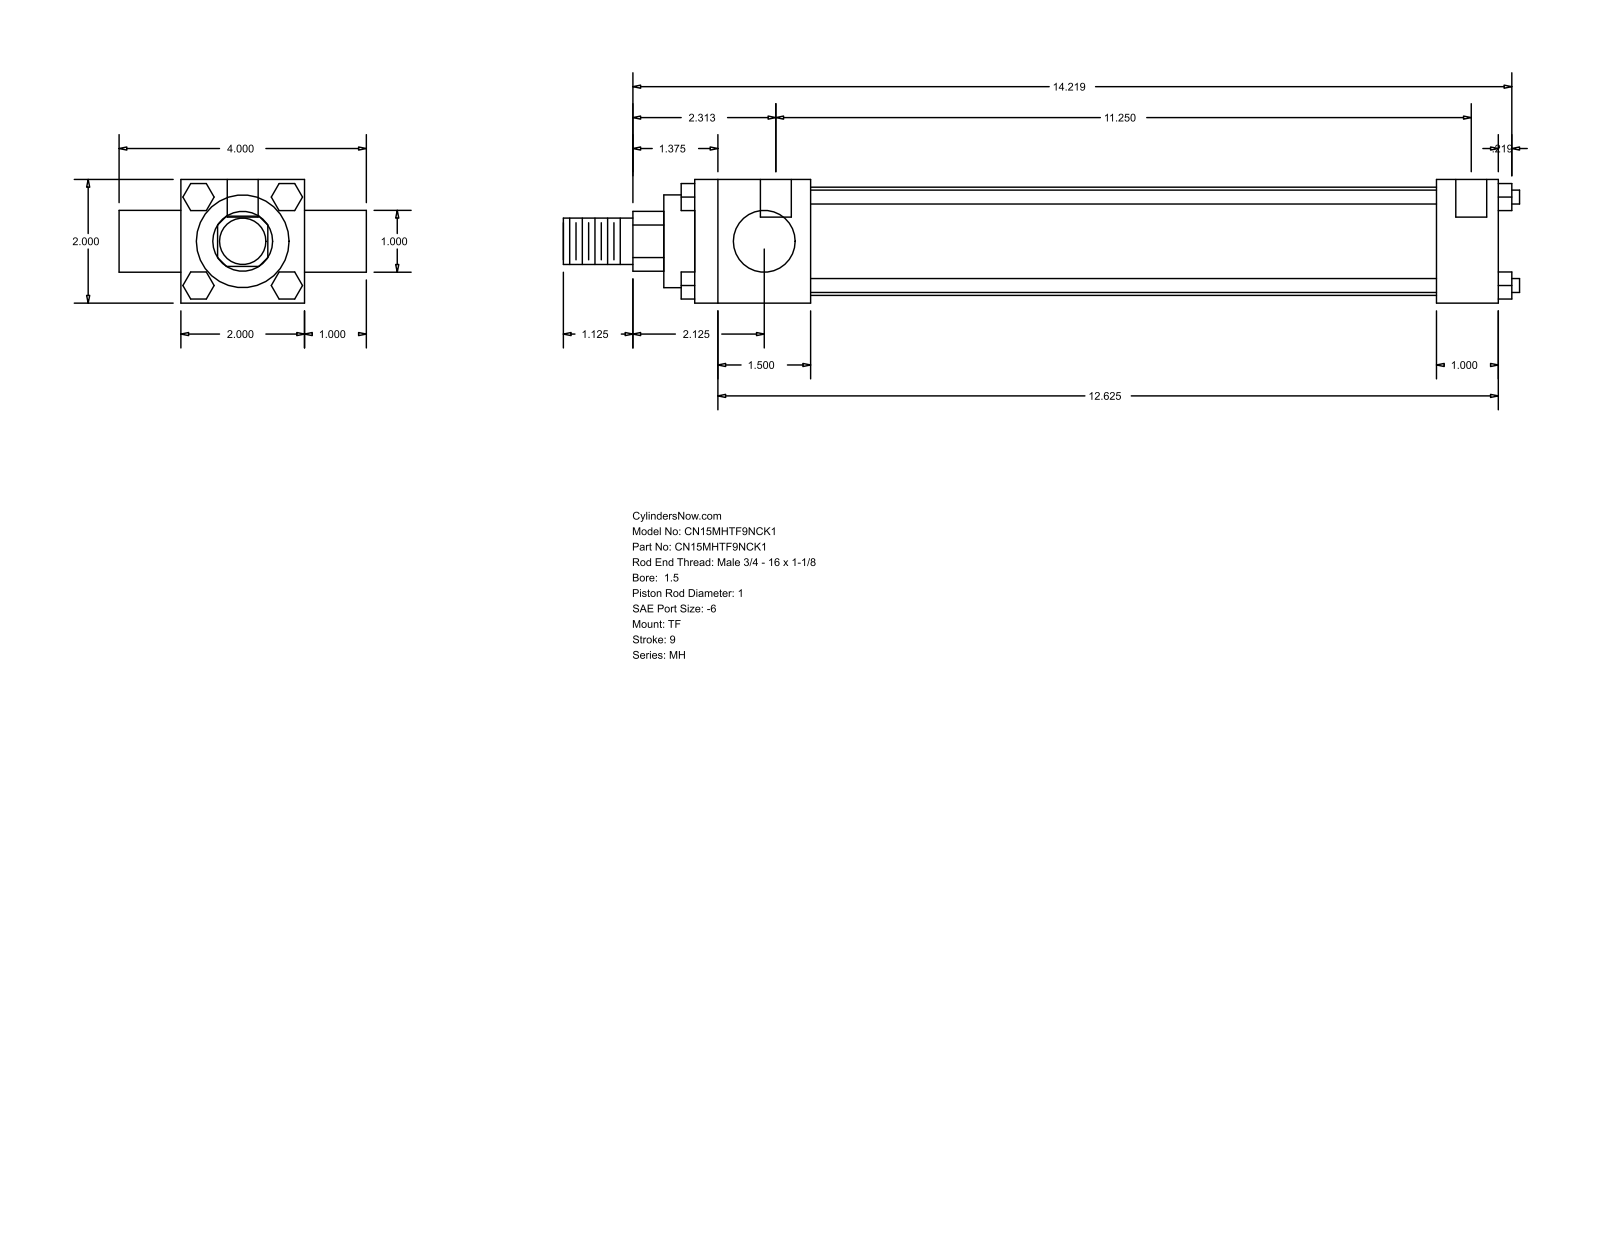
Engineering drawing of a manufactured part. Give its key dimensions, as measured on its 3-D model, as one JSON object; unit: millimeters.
{"part_name": "MH_TF__0150_1", "step_written_by": "GSSL Pune (CONFIG_CONTROL_DESIGN)", "units": "millimeters", "bodies": {"solids": 0, "faces": 120, "planar": 92, "cylindrical": 28, "other": 0}, "overall_size": [392.91, 101.6, 50.8], "round_holes": [[5.56, 3], [12.7, 2]], "round_bosses_or_shafts": [[5.71, 4], [25.4, 2], [44.45, 1], [38.1, 1], [19.05, 1]], "partial_cylinders_radius": [[12.29, 1]], "face_to_face_distances": [50.8, 25.4, 330.2, 76.2, 47.63, 282.57, 304.8, 257.17, 101.6, 12.7], "hole_center_spacings": [3.18, 285.75, 288.93]}
